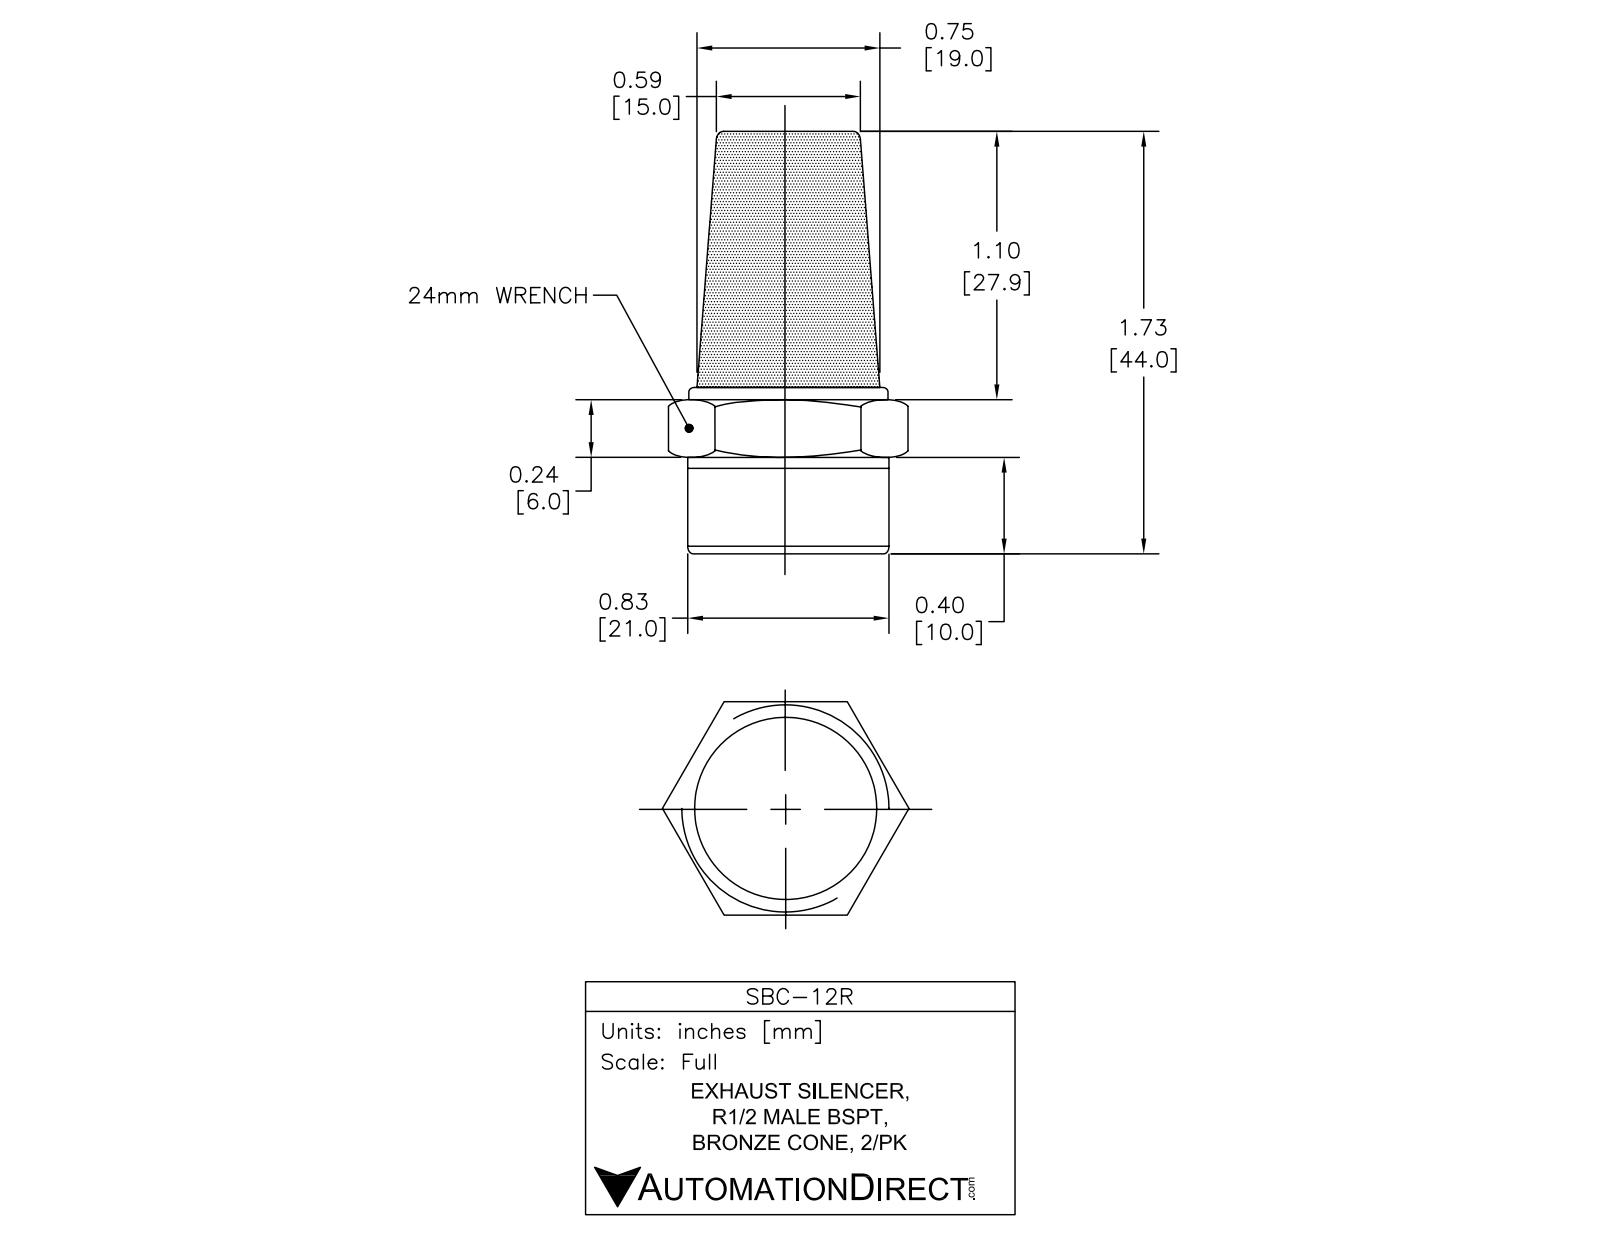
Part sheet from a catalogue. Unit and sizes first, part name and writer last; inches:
Units: inches
Overall size (bounding box): 1.74 × 0.94 × 0.814
Round holes (diameter × count): ⌀0.44 ×1
Round bosses / shafts (diameter × count): ⌀0.78 ×1, ⌀0.703 ×1
Main face-to-face distances: 0.814, 1.74, 1.656, 0.084, 0.4, 1.256, 1.34, 0.667, 0.267, 0.99
Volume: 0.363 in³ · Surface area: 7.964 in²
Bodies: 1 solid, 55 faces (14 planar, 15 cylindrical, 26 other)
Part name (STEP PRODUCT): SBC-12R
STEP written by: SolidWorks 2015 (CONFIG_CONTROL_DESIGN)
